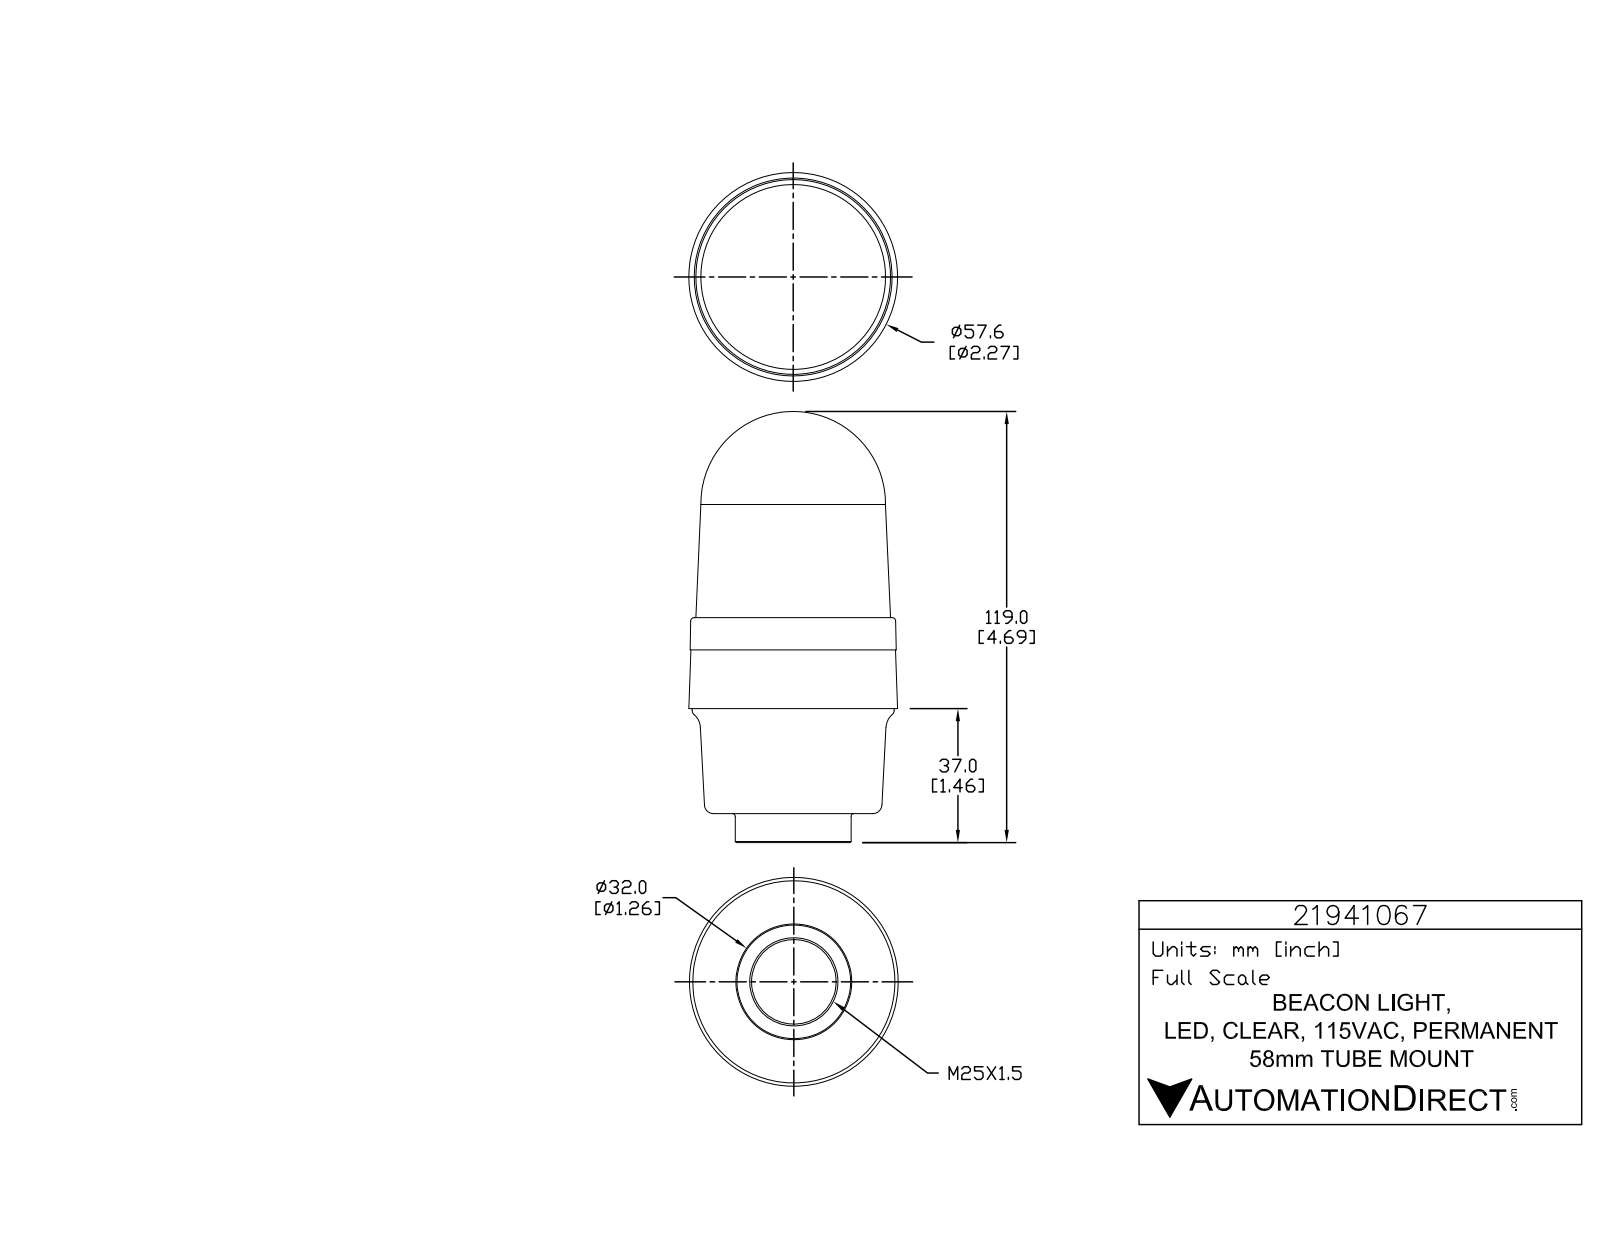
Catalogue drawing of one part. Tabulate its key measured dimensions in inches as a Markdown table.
| quantity | value |
| --- | --- |
| part name | 21941067 |
| STEP written by | SolidWorks 2015 (AUTOMOTIVE_DESIGN) |
| units | inches |
| bodies | 1 solid, 791 faces (525 planar, 168 cylindrical, 98 other) |
| overall size | 4.685 × 2.269 × 2.269 |
| volume | 13.89 in³ |
| surface area | 34.06 in² |
| round holes (diameter × count) | 0.039 × 3, 0.92 × 1 |
| round bosses / shafts (diameter × count) | 0.226 × 3, 0.056 × 3, 2.197 × 1, 1.26 × 1 |
| partial cylindrical surfaces (radius × count) | 0.008 × 6, 0.008 × 6, 0.008 × 6, 0.131 × 6, 0.004 × 3, 0.005 × 3, 0.008 × 3, 0.008 × 3 |
| main face-to-face distances | 0.315, 1.142, 1.457, 0.988, 2.13, 2.445, 0.35, 0.638, 1.78, 2.094 |
